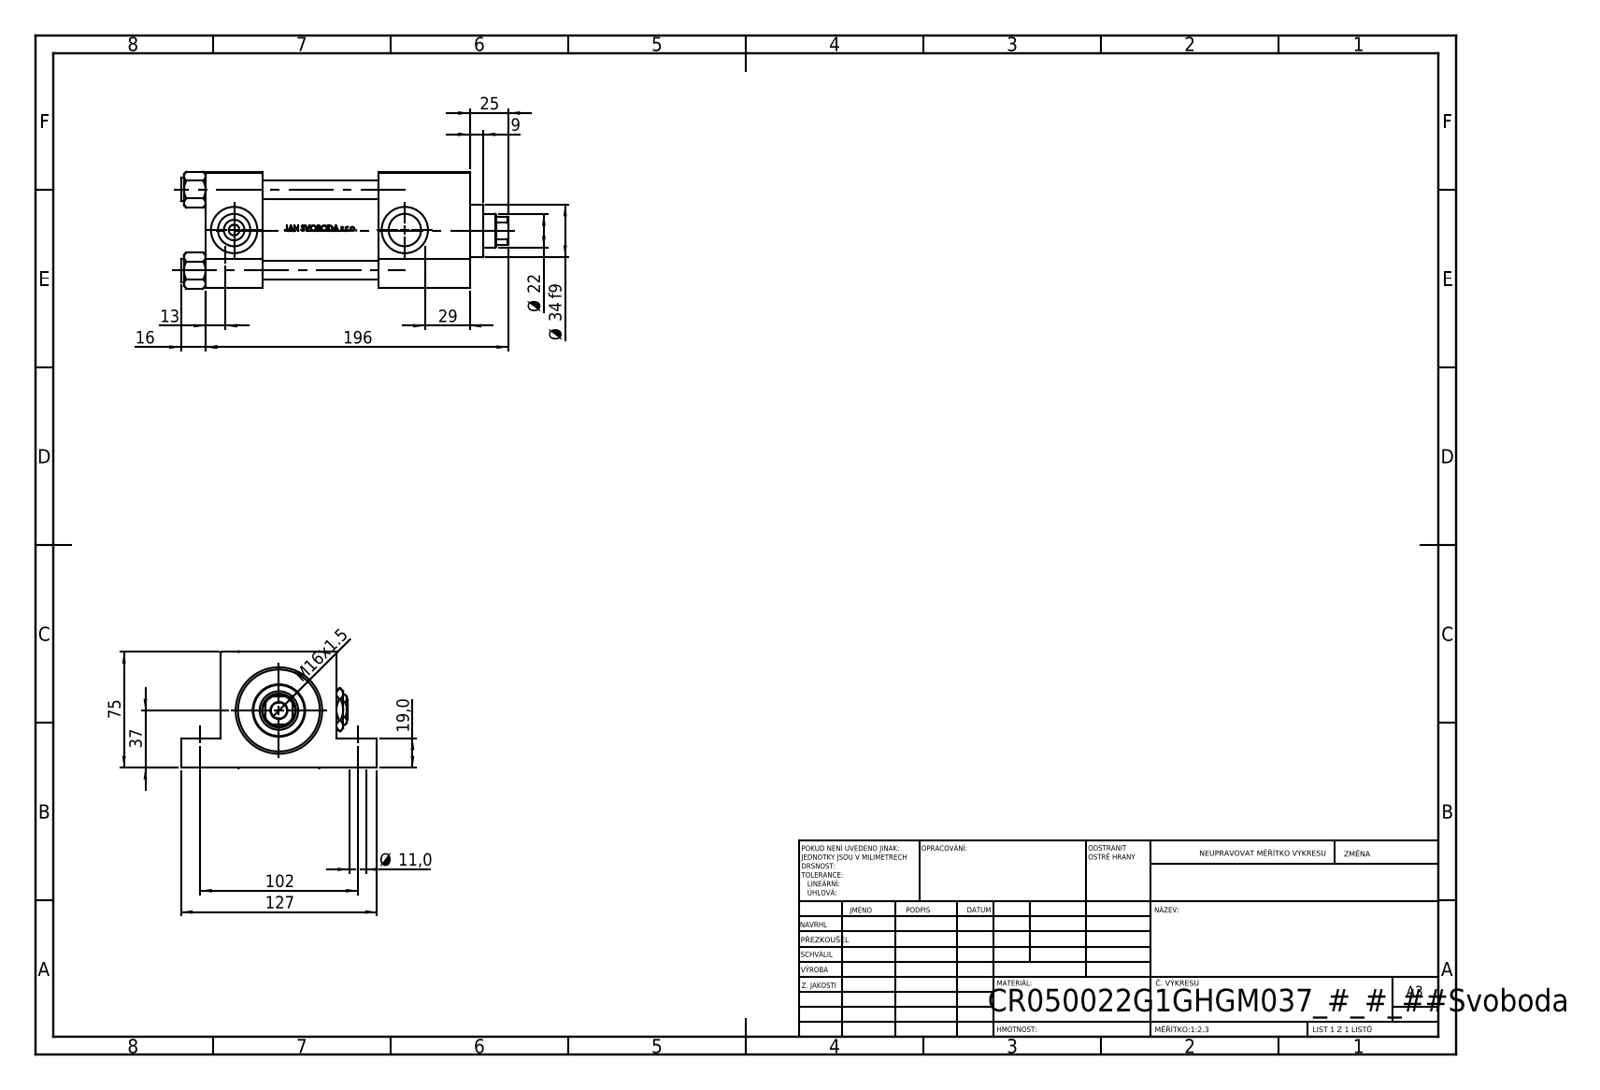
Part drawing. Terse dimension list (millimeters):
name: Zatka_pro_OIL_PORT; V215CR_G_Body; V215CR_G_TYCINKA; V215CR_VCP_G (+2 more)
written by: SolidWorks 2019 (CONFIG_CONTROL_DESIGN)
unit: mm
bodies: 12 solids, 1134 faces (454 planar, 128 cylindrical, 552 other)
size: 212 × 127 × 75.54
volume: 775 048 mm³; area: 170 703 mm²
holes: 4× ⌀11, 4× ⌀12, 2× ⌀7, 2× ⌀20.96, 2× ⌀30, 1× ⌀10.5, 1× ⌀22, 1× ⌀25, 1× ⌀41, 1× ⌀50, 1× ⌀53
bosses: 4× ⌀15, 1× ⌀56, 1× ⌀34
rounds: 1× R10.5
face distances: 75, 37, 171, 134, 19, 56, 112, 59, 26, 101
hole spacings: 52.3, 36.63, 37.34, 73.96, 102, 129, 164.45, 110.5
